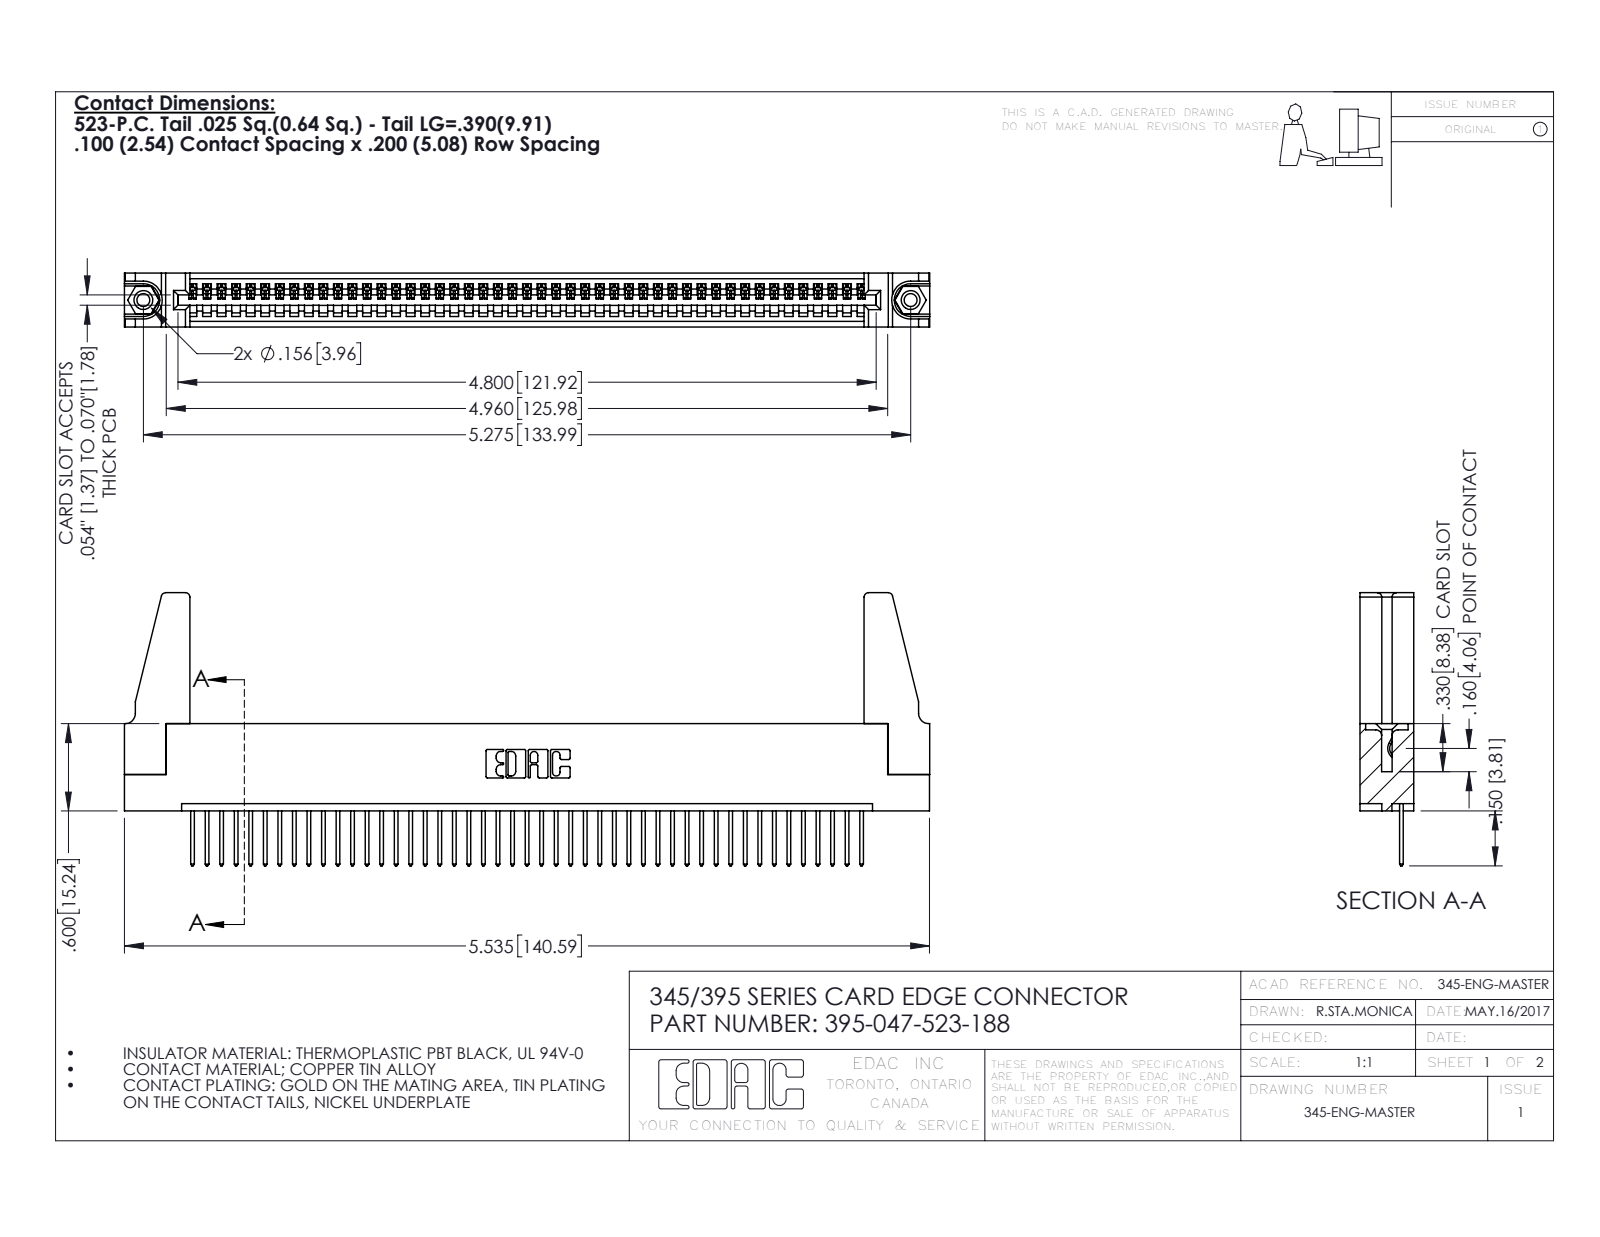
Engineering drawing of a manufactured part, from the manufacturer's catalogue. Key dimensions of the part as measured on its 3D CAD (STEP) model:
Part name (STEP PRODUCT): 345 Part_Flush Mounting Lugs - 0.156 Dia-TH; 345-292-001_345-293-123; 395-047-523-188; 345-220-078_345-220-088 (+1 more)
STEP written by: SolidWorks 2016 (CONFIG_CONTROL_DESIGN)
Units: inches
Bodies: 52 solids, 2976 faces (2032 planar, 928 cylindrical, 16 other)
Overall size (bounding box): 5.536 × 1.877 × 0.37
Volume: 1.015 in³ · Surface area: 32.59 in²
Round holes (diameter × count): ⌀0.089 ×2, ⌀0.125 ×2, ⌀0.156 ×2, ⌀0.064 ×1
Round bosses / shafts (diameter × count): ⌀0.155 ×2
Partial cylindrical surfaces — rounded edges, fillets, slot ends (radius × count): R0.006 ×94, R0.01 ×94, R0.01 ×22, R0.03 ×8, R0.007 ×6, R0.031 ×6, R0.026 ×3, R0.031 ×2
Main face-to-face distances: 0.072, 0.298, 0.37, 0.2, 0.098, 0.272, 0.025, 0.225, 0.149, 0.072
Hole centre spacings: 0.27, 5.039, 5.275
